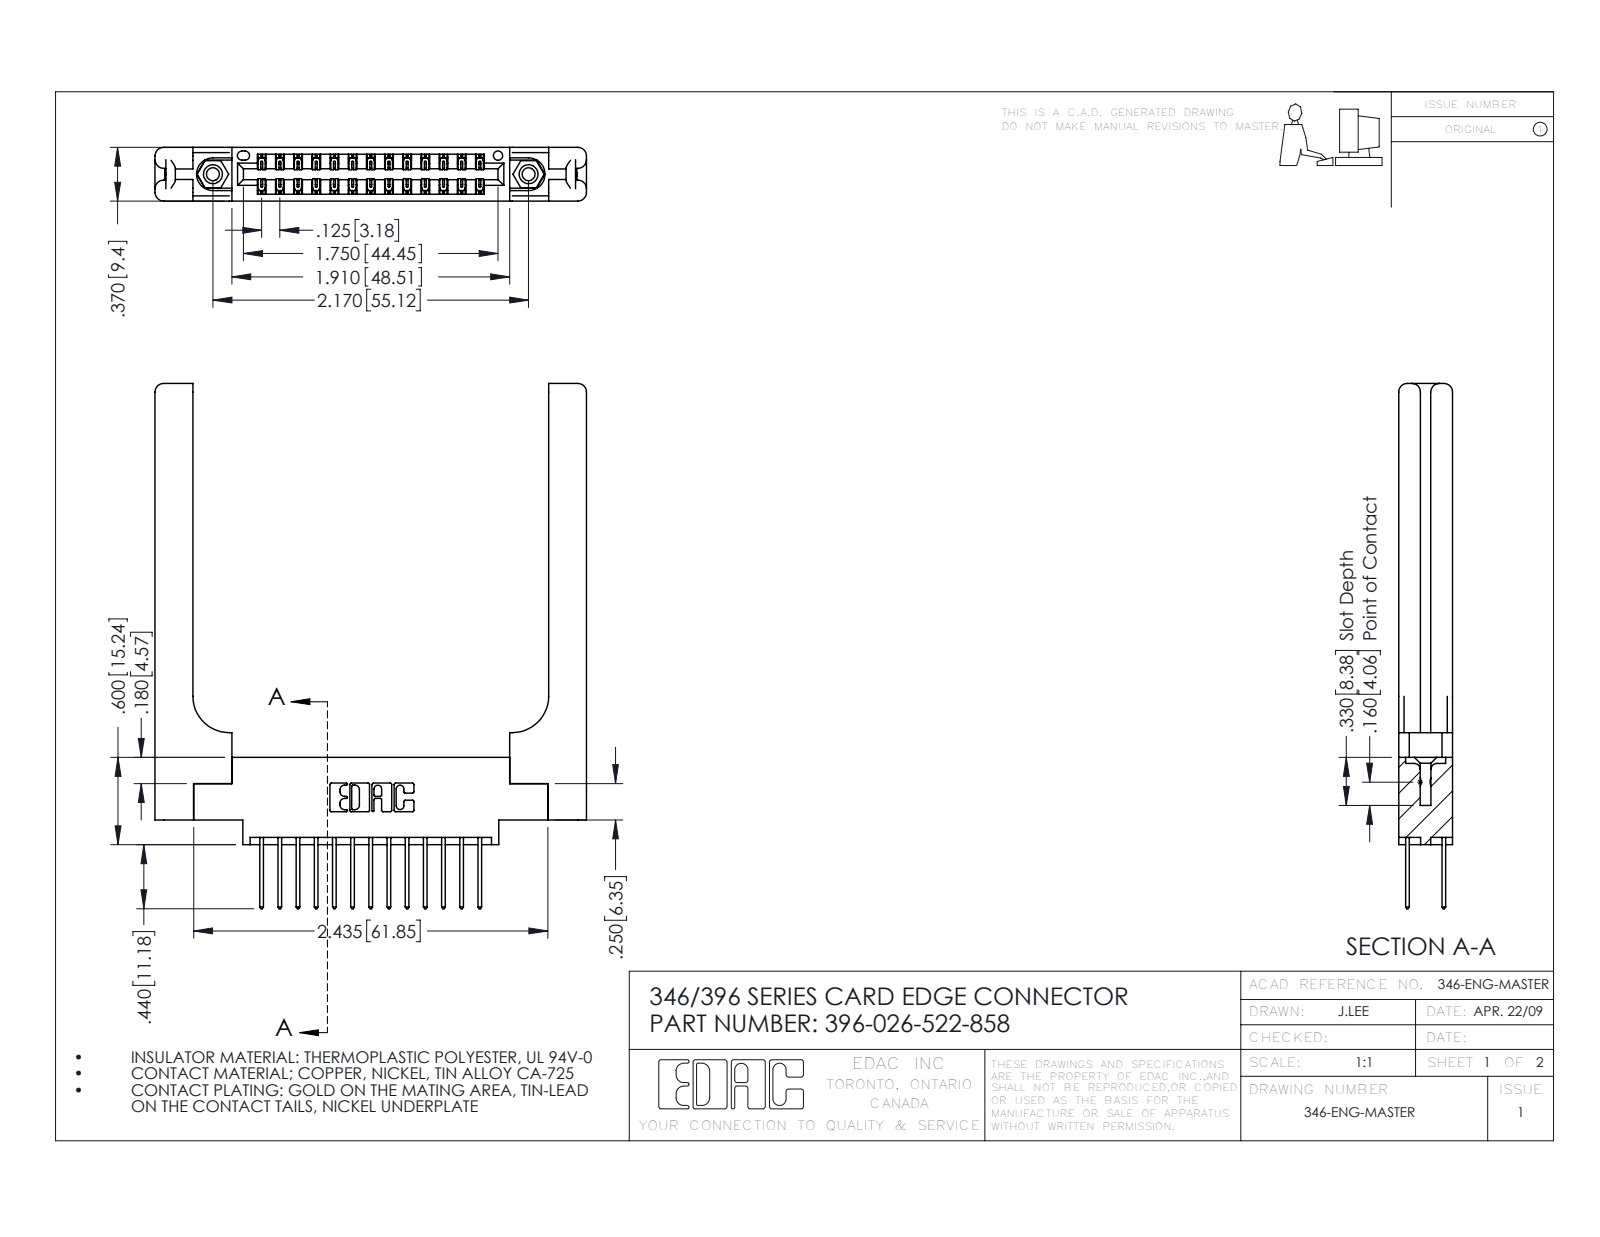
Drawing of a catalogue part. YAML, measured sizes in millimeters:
part_name: "345-292-001_345-293-122; 345-250-001_345-250-001-102; 346-220-058_345-220-058; 346 Part_0.170 Offset - 0.156 Dia-TH (+1 more)"
step_written_by: "SolidWorks 2016 (CONFIG_CONTROL_DESIGN)"
units: millimeters
bodies: {solids: 31, faces: 1734, planar: 1138, cylindrical: 536, other: 60}
overall_size: [91.7, 75.3, 9.4]
volume: 14500
surface_area: 14670
round_holes:
  - {diameter: 2.3, count: 2}
  - {diameter: 3.2, count: 2}
  - {diameter: 4, count: 2}
  - {diameter: 1.6, count: 1}
round_bosses_or_shafts:
  - {diameter: 3.9, count: 2}
partial_cylinders:
  - {radius: 0.2, count: 39}
  - {radius: 0.3, count: 26}
  - {radius: 0.3, count: 22}
  - {radius: 1.5, count: 16}
  - {radius: 0.2, count: 6}
  - {radius: 0.8, count: 6}
  - {radius: 0.7, count: 3}
  - {radius: 0.4, count: 2}
face_to_face_distances: [9.4, 1.8, 3.8, 3.8, 1.2, 8.2, 6.4, 2, 2.6, 5.6]
hole_center_spacings: [6.2, 49.9, 55.1]
